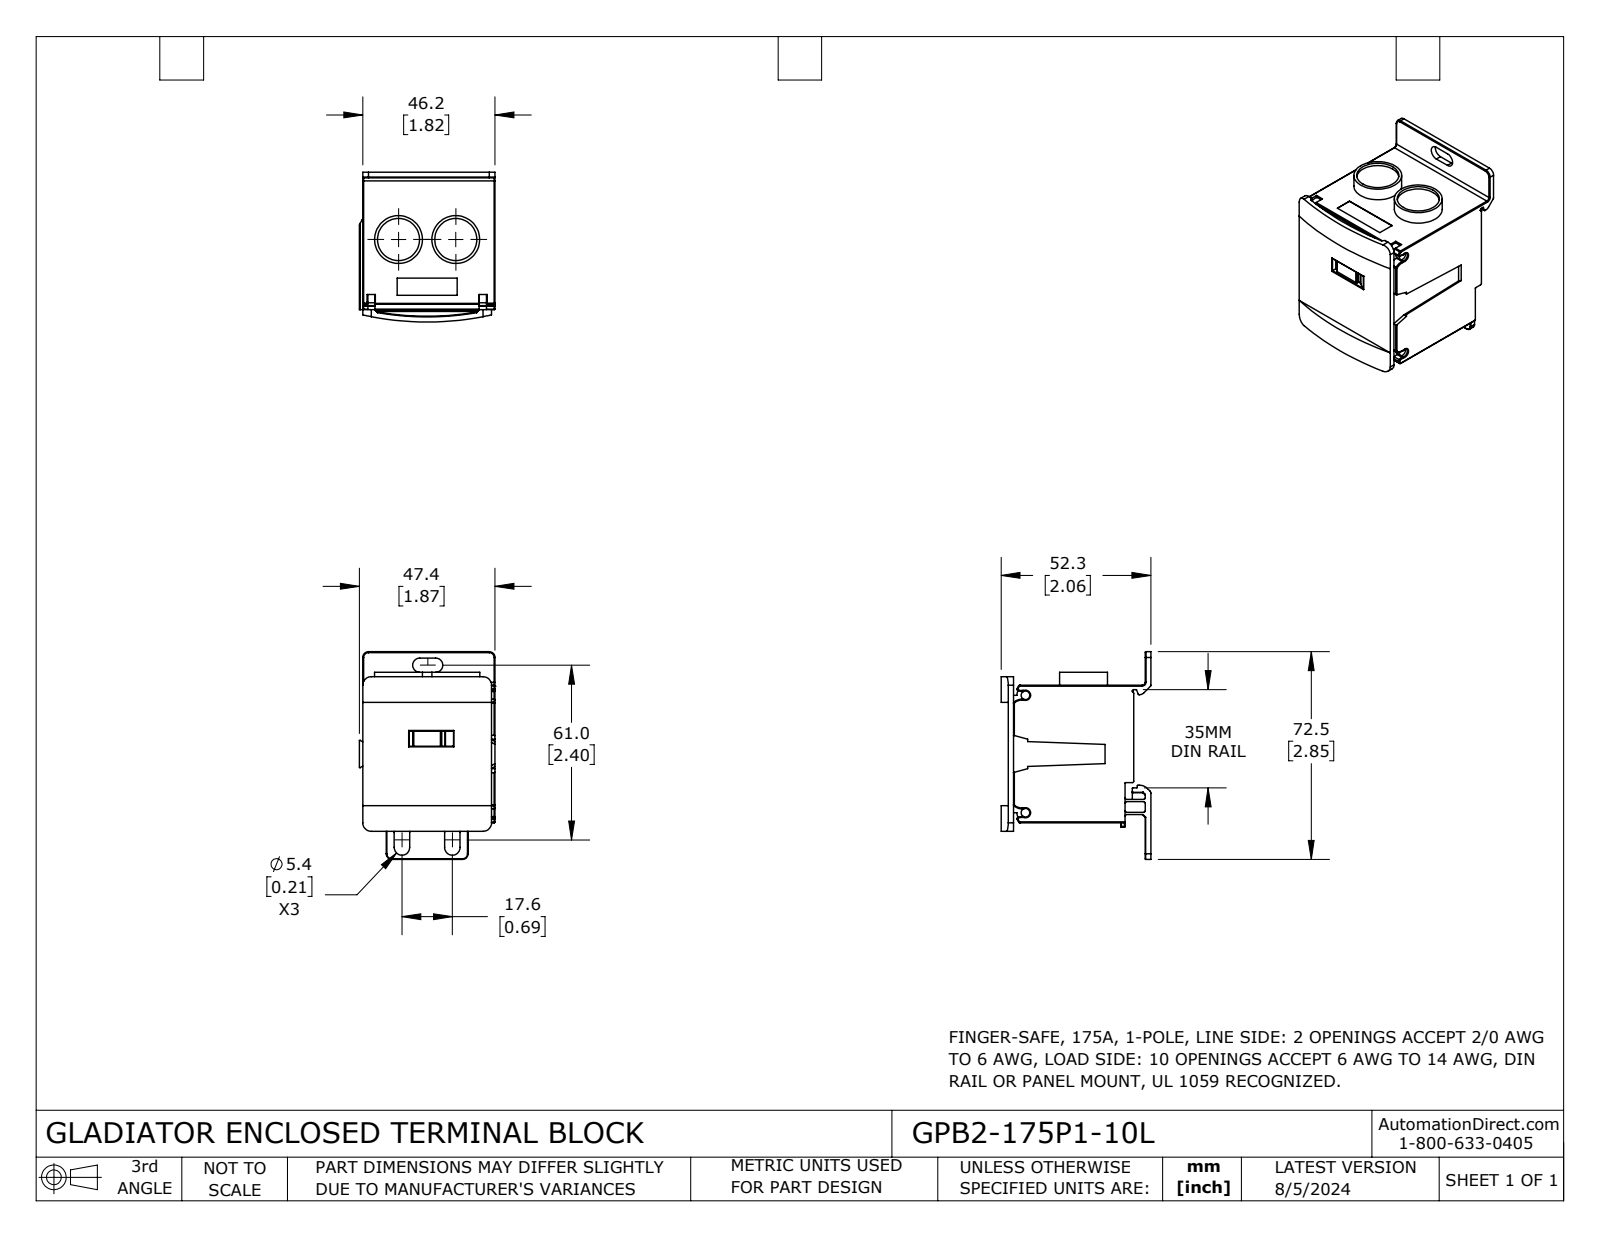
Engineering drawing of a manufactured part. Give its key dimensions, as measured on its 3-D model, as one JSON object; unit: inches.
{"part_name": "GPB2-175P1-10L", "step_written_by": "SolidWorks 2023 (CONFIG_CONTROL_DESIGN)", "units": "inches", "bodies": {"solids": 1, "faces": 483, "planar": 168, "cylindrical": 251, "other": 64}, "overall_size": [2.854, 2.059, 1.866], "volume_in3": 6.037, "surface_area_in2": 30.7, "round_holes": [[0.118, 2], [0.579, 2]], "round_bosses_or_shafts": [[0.657, 2]], "partial_cylinders_radius": [[0.008, 83], [0.012, 21], [0.02, 19], [0.118, 6], [0.079, 5], [0.197, 5], [0.207, 5], [0.106, 4]], "face_to_face_distances": [1.819, 0.236, 1.724, 1.89, 1.961, 0.079, 0.02, 0.157, 1.882, 1.87], "hole_center_spacings": [0.787, 1.614]}
